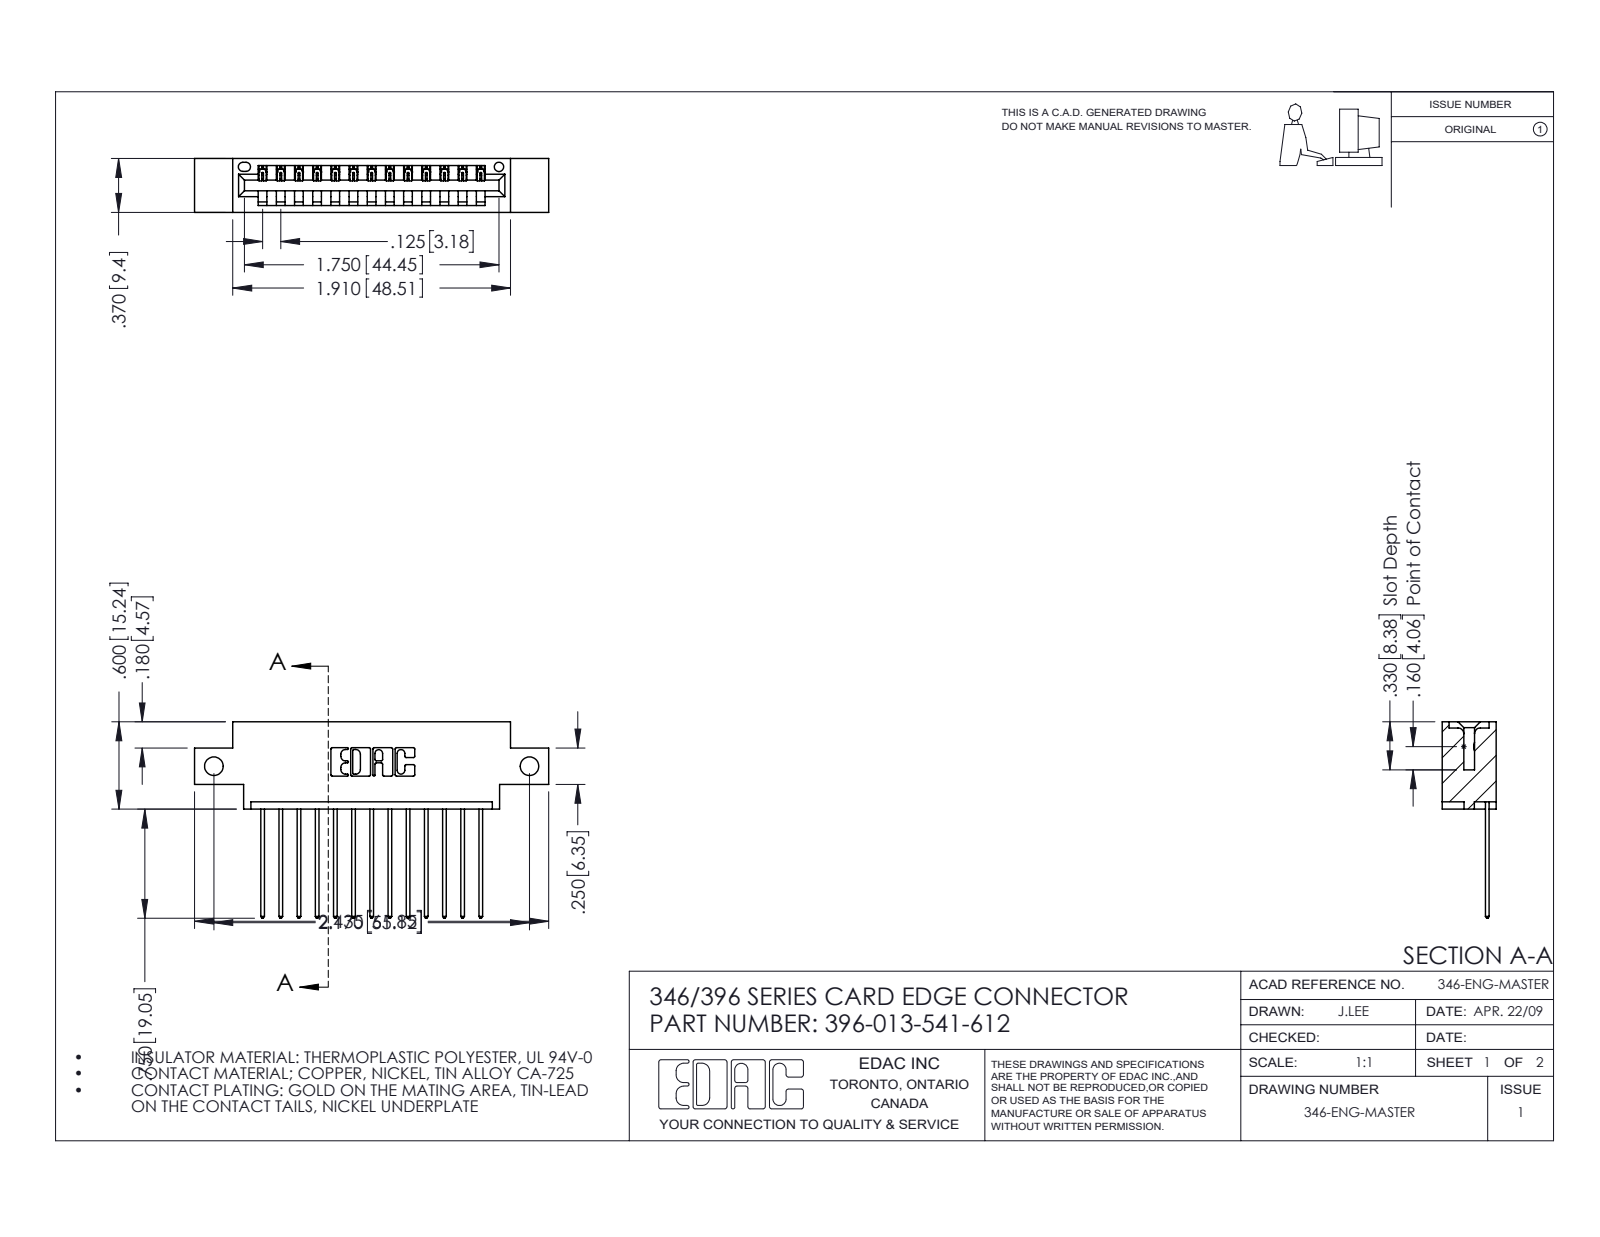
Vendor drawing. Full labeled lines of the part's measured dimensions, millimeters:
Part name (STEP PRODUCT): 396-013-541-612; 346 Part_0.170 Offset - Side Mount; 345-292-001_345-293-141
STEP written by: SolidWorks 2016 (CONFIG_CONTROL_DESIGN)
Units: millimetres
Bodies: 14 solids, 880 faces (600 planar, 280 cylindrical, 0 other)
Overall size (bounding box): 61.8 × 34.3 × 9.4
Volume: 5 520 mm³ · Surface area: 6 858 mm²
Round holes (diameter × count): ⌀3.3 ×2, ⌀1.6 ×1
Partial cylindrical surfaces — rounded edges, fillets, slot ends (radius × count): R0.2 ×26, R0.3 ×26, R0.3 ×22, R0.2 ×6, R0.8 ×6, R0.7 ×3, R0.8 ×2, R1 ×2
Main face-to-face distances: 1.2, 8.2, 6.4, 9.4, 1.8, 7.6, 0.6, 3.8, 5.6, 2.5
Hole centre spacings: 55.1
